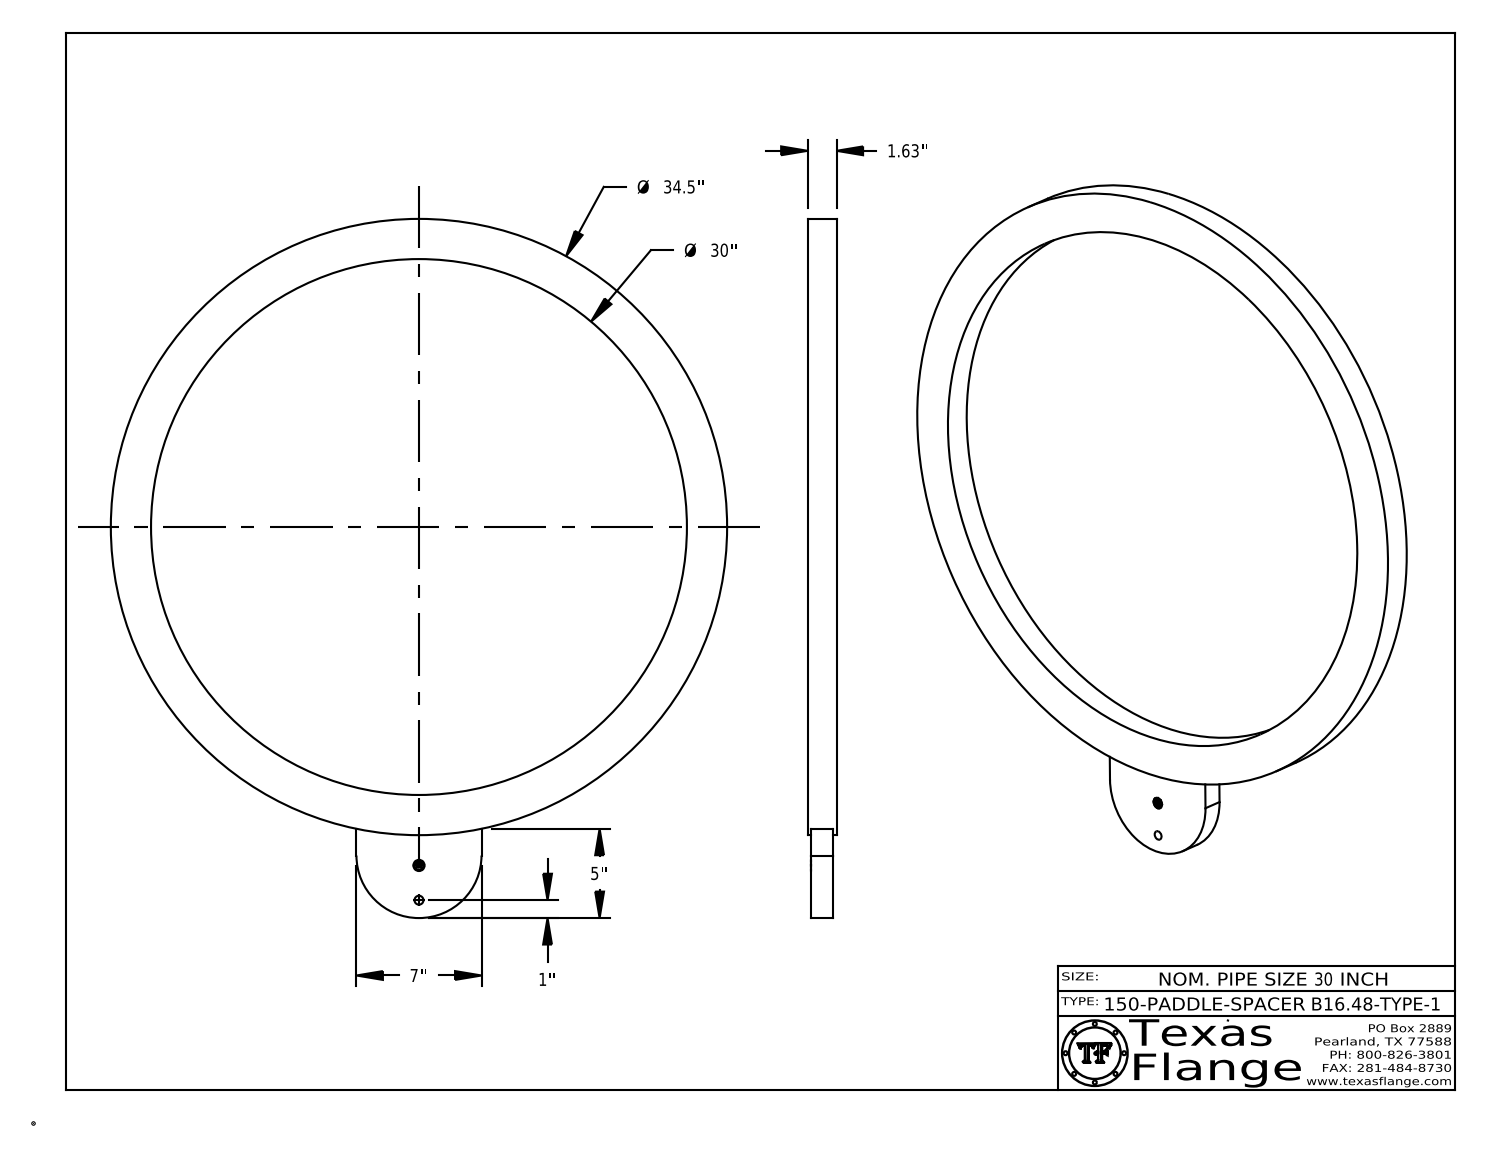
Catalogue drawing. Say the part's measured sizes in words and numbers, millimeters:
The part is named "30-150-PADDLE-SPACER-B16.48-TYPE-2". Its 3-D file was written by "CATIA V5 STEP AP214 (AUTOMOTIVE_DESIGN)". It is 1 solid with 398 faces: 371 planar, 27 cylindrical and 0 other. Overall it measures 994.2 by 876.3 by 41.3 millimeters. Its volume is 6 627 000 cubic millimeters and its surface area 549 300 square millimeters. Round holes: 1 of diameter 12.7, 1 of diameter 15.9, 1 of diameter 762. Round bosses or shafts: 8 of diameter 1, 1 of diameter 876.3, 1 of diameter 12.5. Partial cylindrical surfaces (rounded edges, fillets, slot ends): 1 of radius 88.9. The main face-to-face distances are 41.3, 5.2, 36.1, 31, 177.8, 35.7, 30.6, 0.4, 5.5, 87.3. The hole center spacings are 49.4, 481.2, 530.6.
